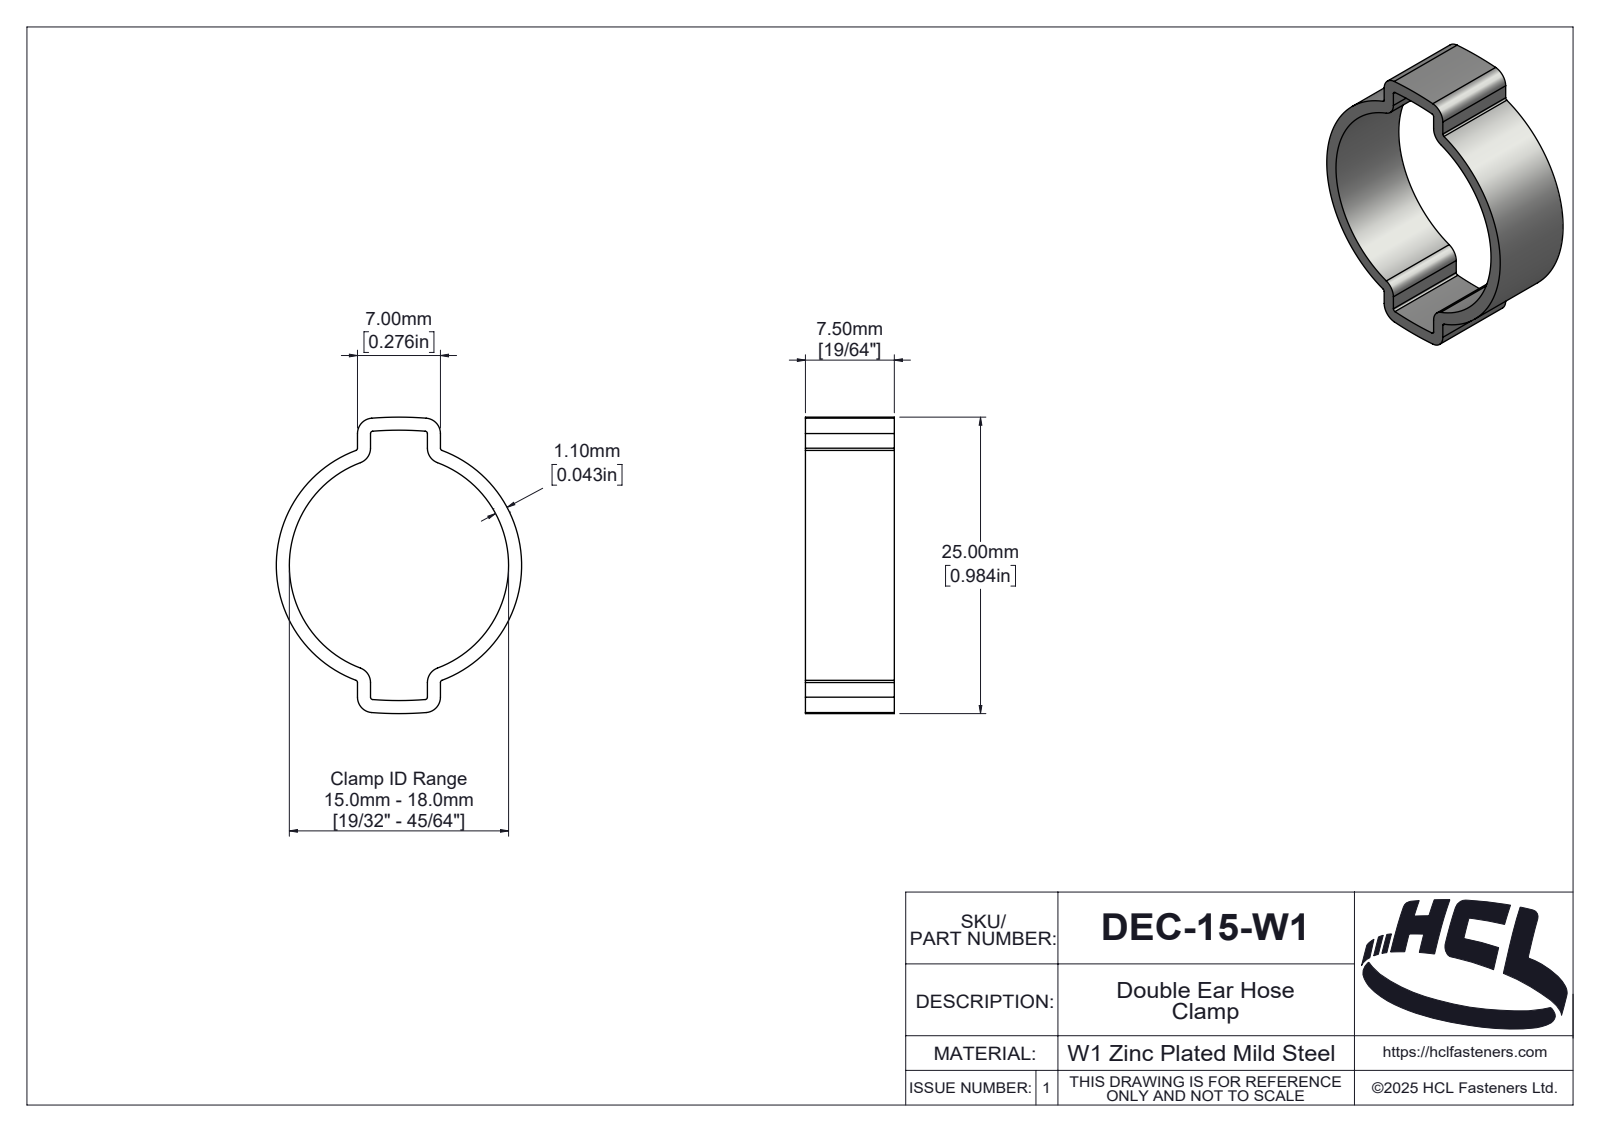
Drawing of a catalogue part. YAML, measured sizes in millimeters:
part_name: "DEC-15-W1"
step_written_by: "SolidWorks 2025 (AUTOMOTIVE_DESIGN)"
units: millimeters
bodies: {solids: 1, faces: 137, planar: 12, cylindrical: 67, other: 58}
overall_size: [25, 20.7, 7.5]
volume: 574
surface_area: 1201
partial_cylinders:
  - {radius: 0.2, count: 8}
  - {radius: 1.3, count: 8}
  - {radius: 28.85, count: 2}
  - {radius: 29.95, count: 2}
  - {radius: 0.2, count: 1}
  - {radius: 0.81, count: 1}
  - {radius: 1.01, count: 1}
  - {radius: 1.06, count: 1}
face_to_face_distances: [7.5, 1.1, 5.9, 7, 4.8, 3.38, 2.28, 2.52, 3.62, 3.23]
